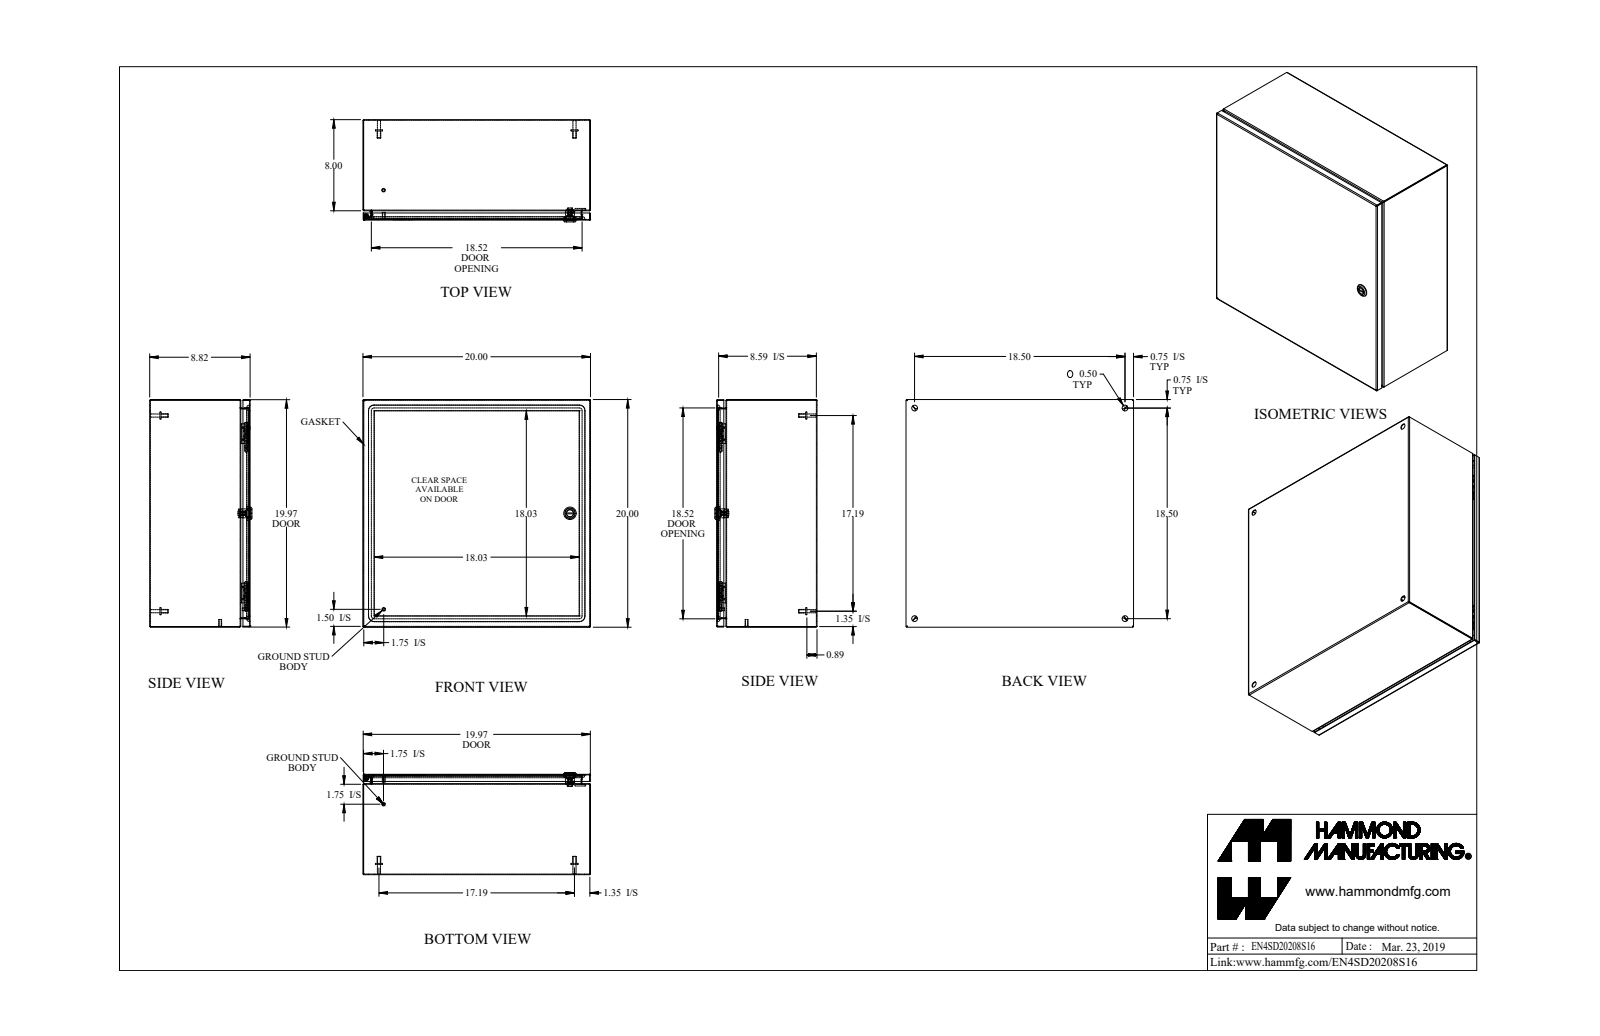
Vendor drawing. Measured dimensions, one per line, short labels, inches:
name: EN4SD20208S16_Default
written by: SolidWorks 2019 (CONFIG_CONTROL_DESIGN)
unit: in
bodies: 22 solids, 656 faces (303 planar, 211 cylindrical, 142 other)
size: 20 × 20 × 8.981
volume: 98.84 in³; area: 3 372 in²
holes: 5× ⌀0.5, 1× ⌀0.172, 1× ⌀0.197, 1× ⌀0.24, 1× ⌀0.242, 1× ⌀0.387, 1× ⌀0.63, 1× ⌀0.768
bosses: 6× ⌀0.313, 5× ⌀0.625, 4× ⌀0.275, 2× ⌀0.25, 1× ⌀1.1, 1× ⌀0.785, 1× ⌀0.525, 1× ⌀0.475
rounds: 21× R0.029, 21× R0.086, 12× R0.188, 4× R0.006, 4× R0.062, 4× R0.25, 4× R0.499, 2× R0.125
face distances: 0.057, 19.943, 0.057, 8.707, 8.764, 8.764, 8.821, 19.886, 20, 7.943
hole spacings: 18.5, 9.31, 19.742, 26.163
